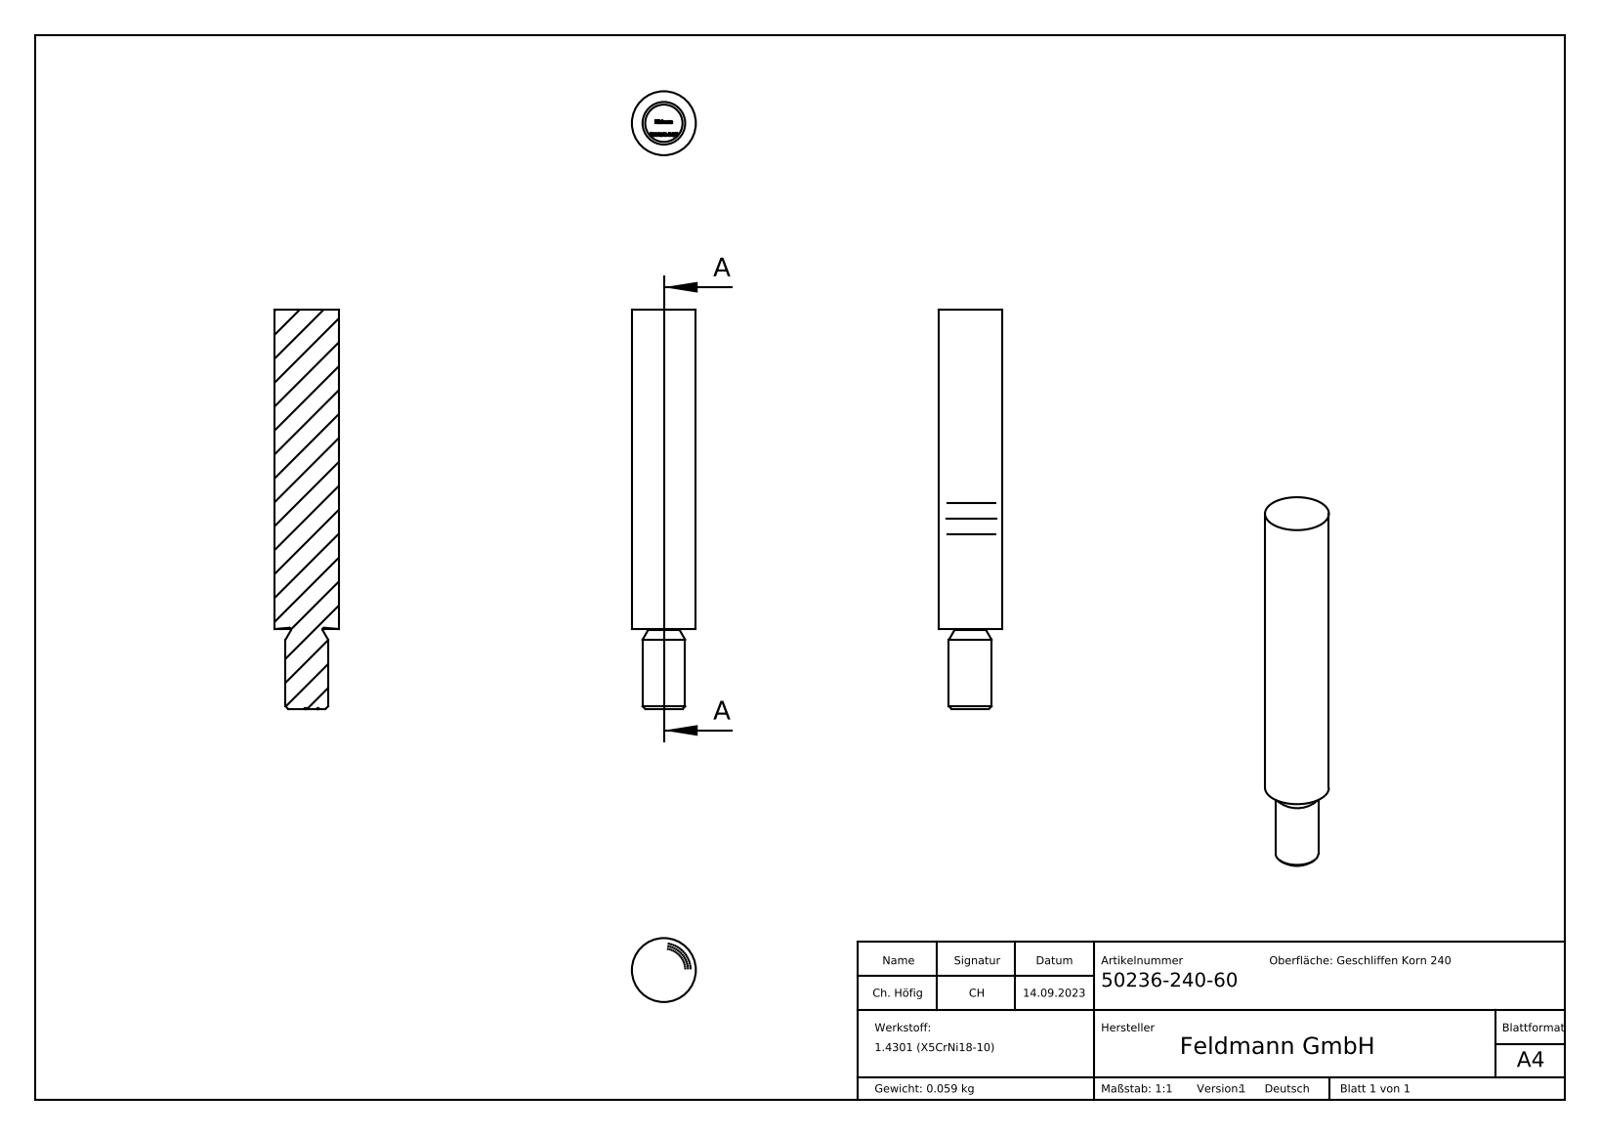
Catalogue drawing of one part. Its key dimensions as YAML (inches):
part_name: "50236-240-60"
step_written_by: "SolidWorks 2018 (CONFIG_CONTROL_DESIGN)"
units: inches
bodies: {solids: 1, faces: 266, planar: 157, cylindrical: 2, other: 107}
overall_size: [2.953, 0.472, 0.472]
volume: 0.458
surface_area: 4.473
round_bosses_or_shafts:
  - {diameter: 0.472, count: 1}
  - {diameter: 0.315, count: 1}
face_to_face_distances: [2.953, 2.949, 0.03, 0.051, 0.094, 0.094, 0.028, 0.061, 0.096, 0.022]
